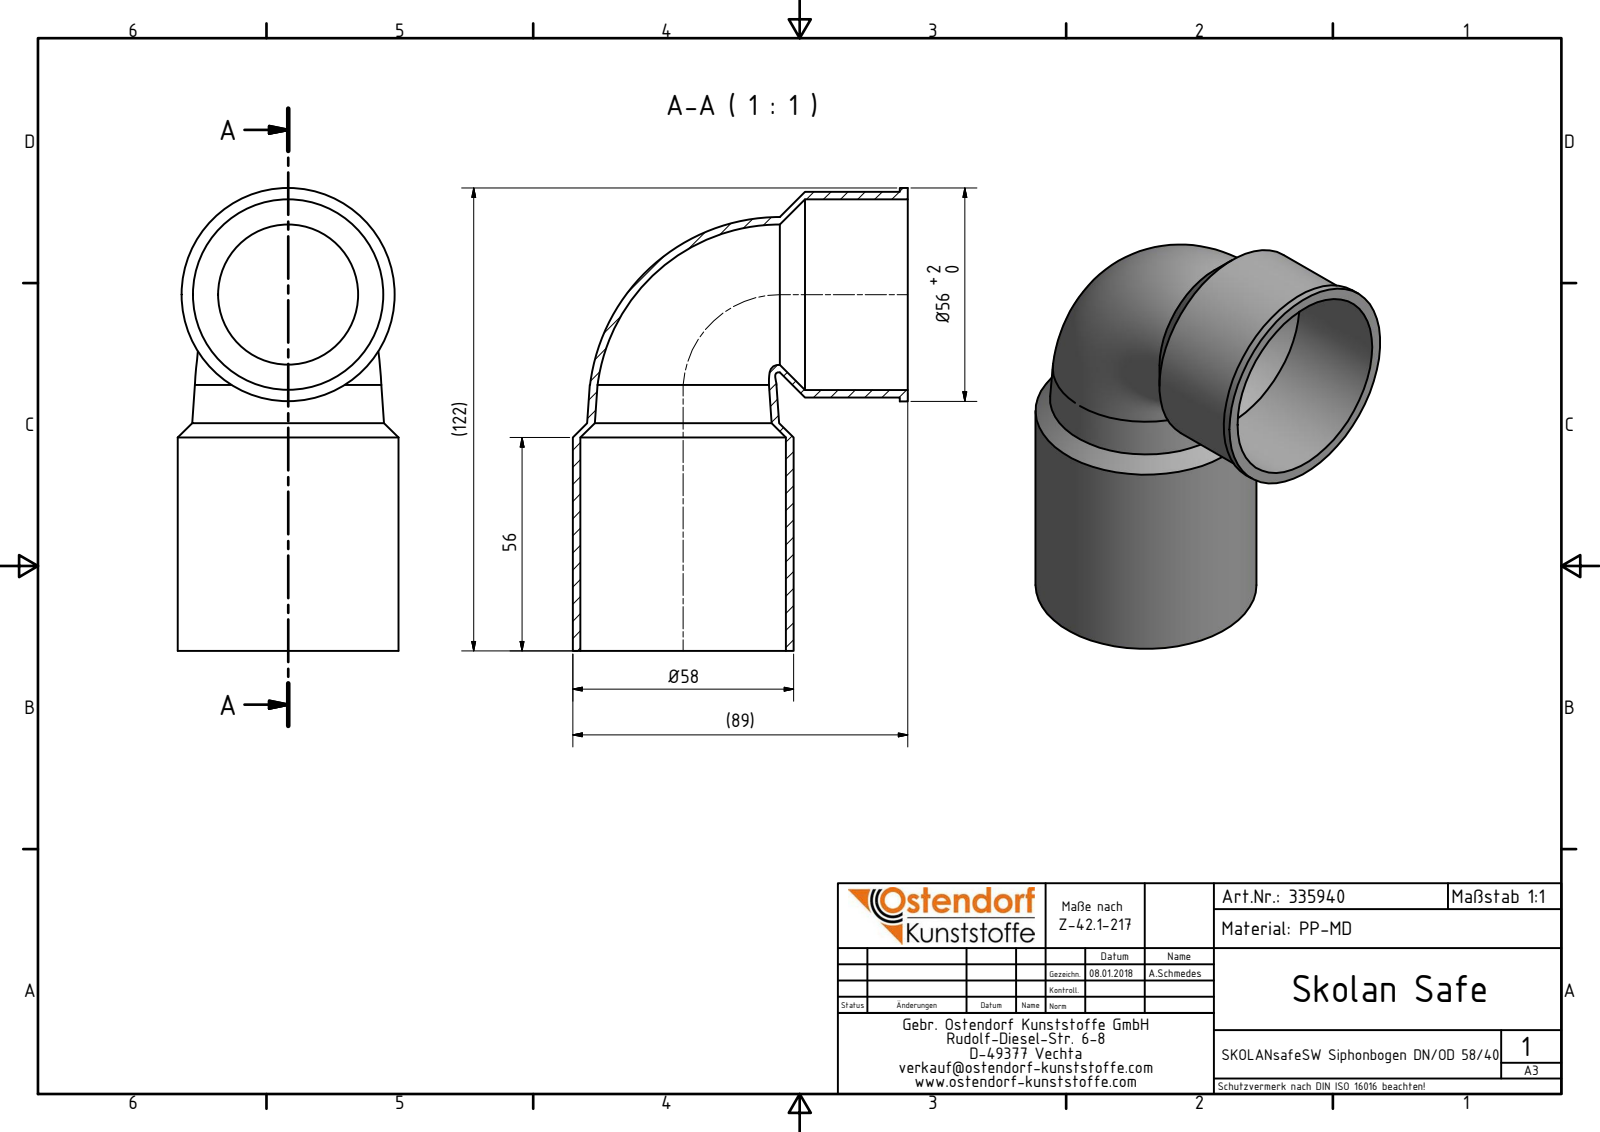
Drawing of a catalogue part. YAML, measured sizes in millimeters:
part_name: "335940 SKOLANsafeSW Siphonbogen DN_OD 58_40"
step_written_by: "Autodesk Inventor 2016 (AUTOMOTIVE_DESIGN)"
units: millimeters
bodies: {solids: 1, faces: 16, planar: 3, cylindrical: 5, other: 8}
overall_size: [121.5, 88, 58]
volume: 45136
surface_area: 47203
round_holes:
  - {diameter: 50, count: 1}
  - {diameter: 54, count: 1}
round_bosses_or_shafts:
  - {diameter: 58, count: 1}
  - {diameter: 56, count: 1}
  - {diameter: 54, count: 1}
face_to_face_distances: [2.1]
